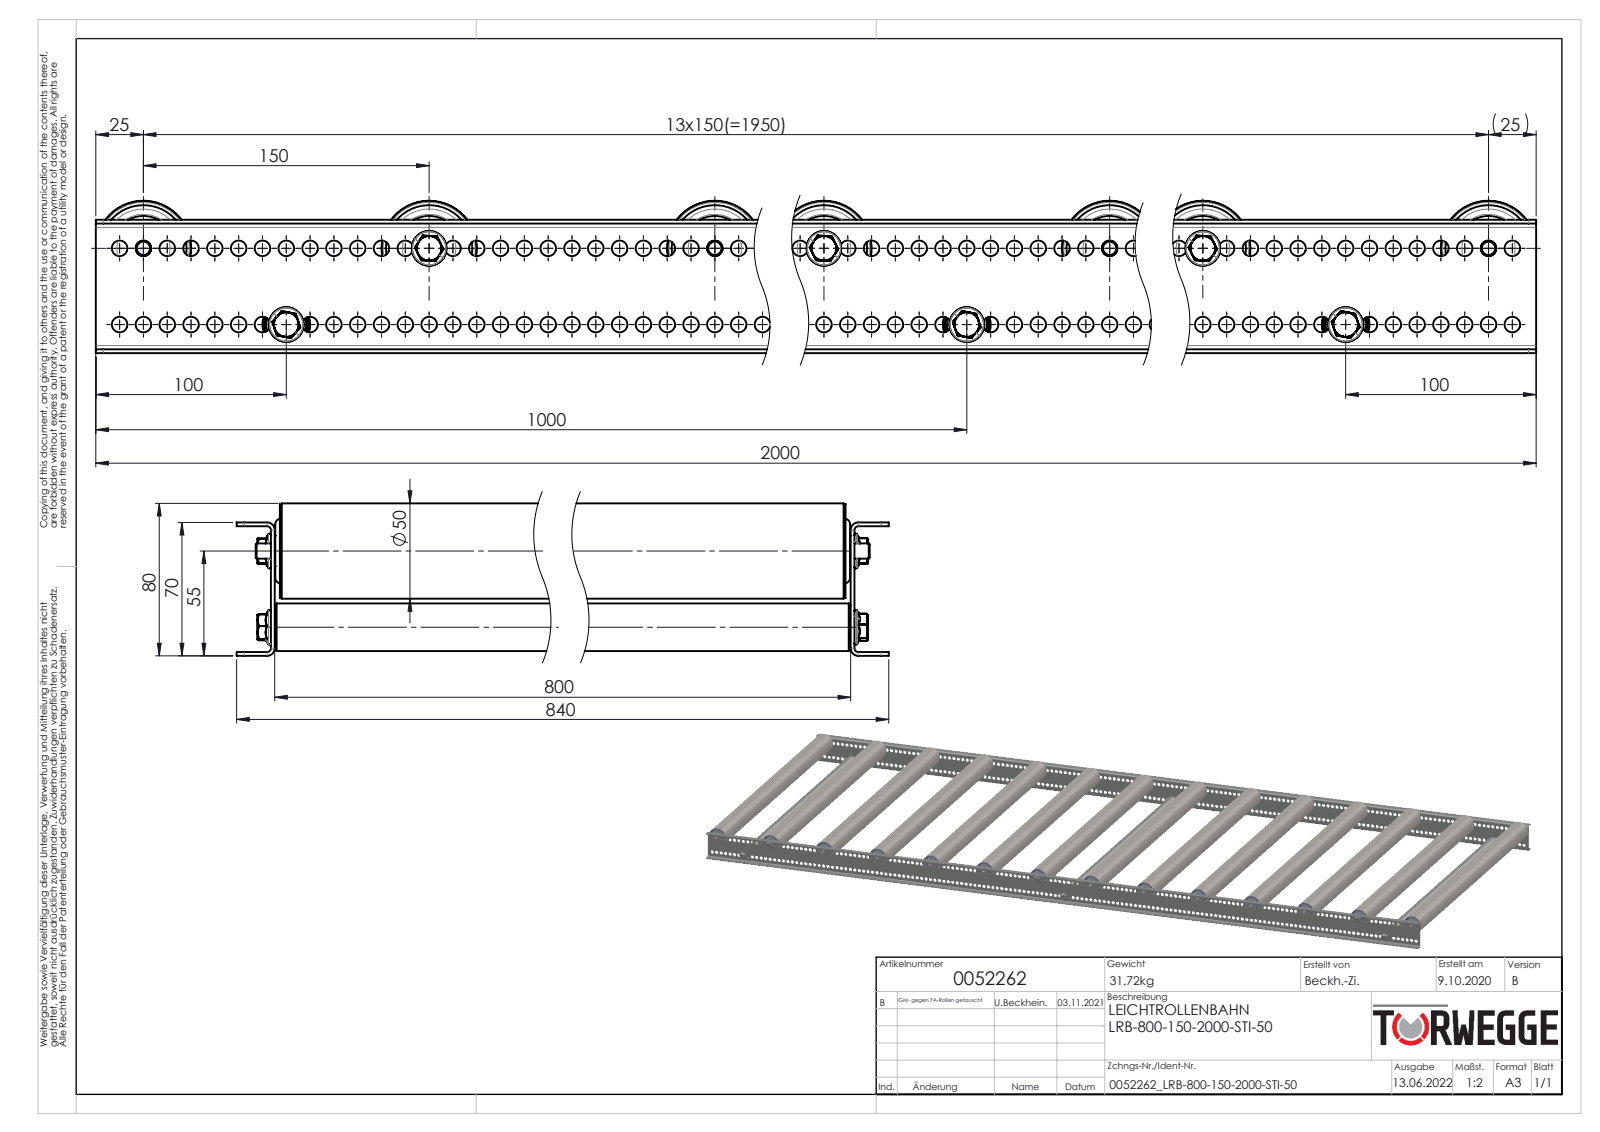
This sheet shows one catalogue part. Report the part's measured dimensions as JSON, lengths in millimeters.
{"part_name": "Druckfeder_1,2x10x30; Tragrollenachse-Ø8_KFG_L=820; Profil_LRB-20x70x20x2_KFG_S100202_U-PROFIL-20-70-20-2-LRB-L=2000; TRG-50x1,5-STI-A8-FA_KFG_0054467_TRG-50x1,5-STI-A8-FA-EL=800 (+8 more)", "step_written_by": "SolidWorks 2020 (AUTOMOTIVE_DESIGN)", "units": "millimeters", "bodies": {"solids": 350, "faces": 6934, "planar": 1320, "cylindrical": 2752, "other": 2862}, "overall_size": [2000, 840, 80], "volume_mm3": 4665000, "surface_area_mm2": 5292000, "round_holes": [[8.2, 318], [17.1, 14], [18.5, 14], [27.7, 14], [45.3, 14], [47, 14], [7.6, 11], [6.8, 6], [12, 3], [12.2, 3], [19.2, 3], [21, 3]], "round_bosses_or_shafts": [[8, 17], [50, 14], [49.5, 14], [47.3, 14], [29.7, 14], [27.4, 14], [27.3, 14], [16, 14]], "partial_cylinders_radius": [[0.6, 22], [0.75, 22], [2.45, 22], [2.5, 12], [4.87, 11], [7, 11], [4, 8], [2, 4]], "face_to_face_distances": [2, 802, 68, 800, 804, 70, 66, 18, 20, 820], "hole_center_spacings": [12.5, 25, 37.5, 50, 62.5, 75, 87.5, 100]}
